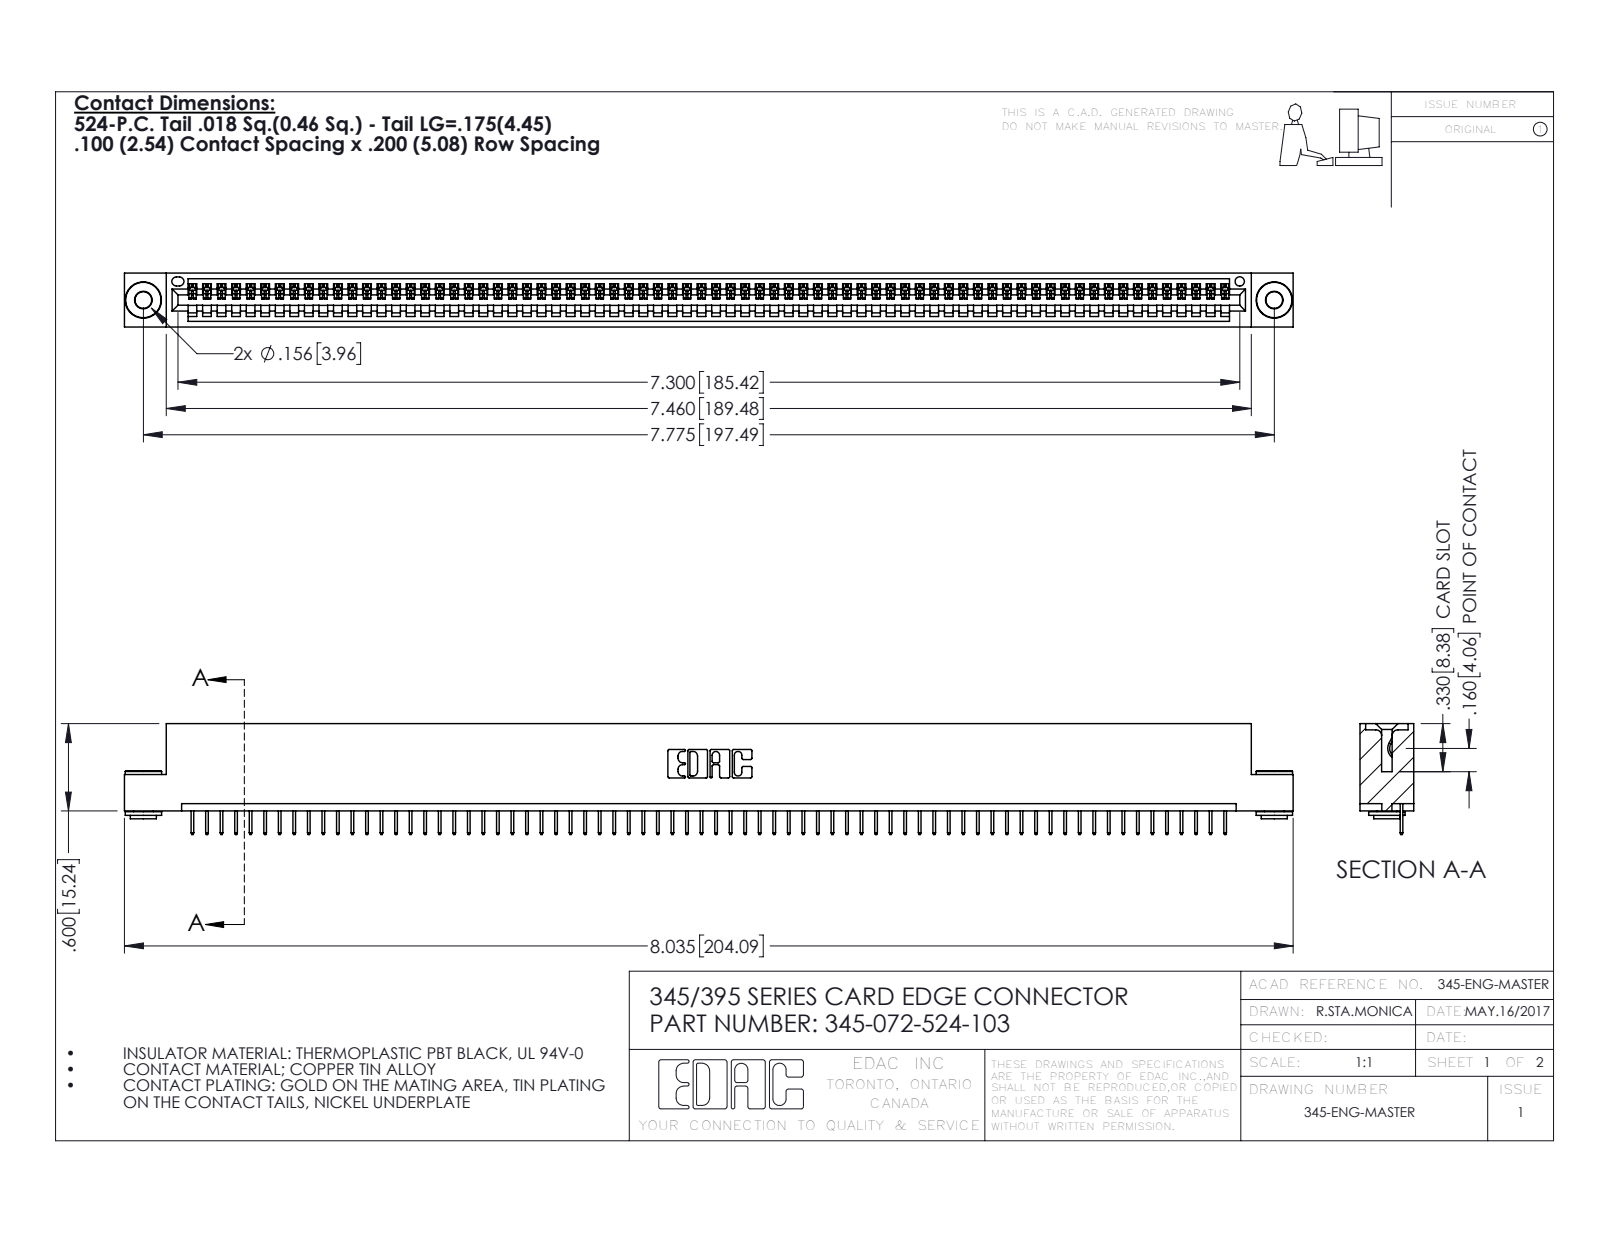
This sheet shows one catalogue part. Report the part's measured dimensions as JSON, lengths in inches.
{"part_name": "345 Part_Flush Mounting Lugs - 0.156 Dia-TH; 345-072-524-103; 345-250-002_345-250-002-102; 345-292-001_345-293-124", "step_written_by": "SolidWorks 2016 (CONFIG_CONTROL_DESIGN)", "units": "inches", "bodies": {"solids": 75, "faces": 4628, "planar": 3402, "cylindrical": 1218, "other": 8}, "overall_size": [8.035, 0.762, 0.37], "volume_in3": 1.182, "surface_area_in2": 39.44, "round_holes": [[0.116, 2], [0.156, 2], [0.064, 1]], "round_bosses_or_shafts": [[0.25, 2], [0.18, 2], [0.136, 2]], "partial_cylinders_radius": [[0.006, 144], [0.01, 22], [0.007, 6], [0.031, 6], [0.026, 3], [0.031, 2], [0.04, 2], [0.014, 1]], "face_to_face_distances": [0.072, 0.298, 0.37, 0.2, 0.025, 0.098, 0.272, 0.225, 0.072, 0.149], "hole_center_spacings": [0.27, 7.539, 7.775]}
